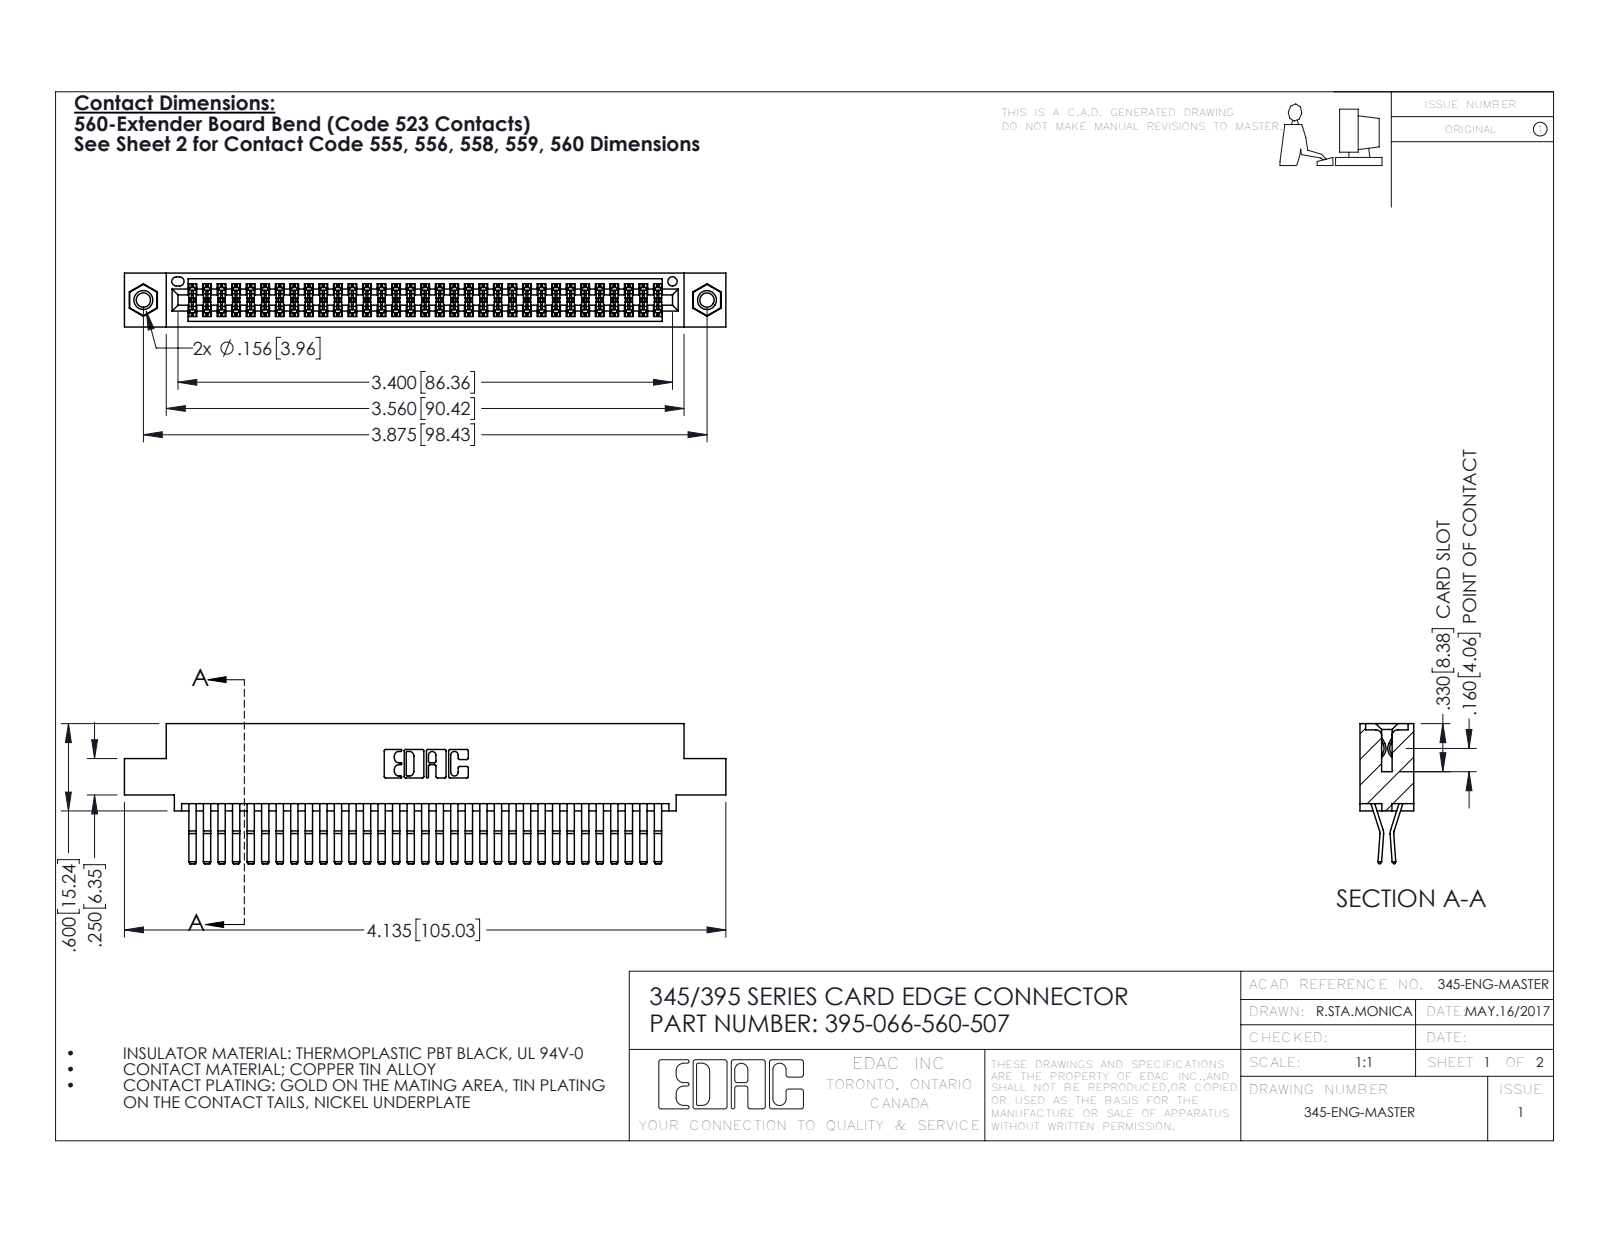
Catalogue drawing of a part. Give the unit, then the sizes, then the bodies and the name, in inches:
Units: inches
Overall size (bounding box): 4.135 × 0.962 × 0.37
Round holes (diameter × count): ⌀0.098 ×2, ⌀0.125 ×2, ⌀0.156 ×2, ⌀0.064 ×1
Round bosses / shafts (diameter × count): ⌀0.155 ×2
Partial cylindrical surfaces — rounded edges, fillets, slot ends (radius × count): R0.006 ×100, R0.01 ×22, R0.007 ×6, R0.031 ×6, R0.026 ×3, R0.01 ×2, R0.014 ×2, R0.019 ×2
Main face-to-face distances: 0.025, 0.072, 0.298, 0.2, 0.37, 0.098, 0.272, 0.225, 0.175, 0.149
Hole centre spacings: 0.27, 3.64, 3.875
Volume: 0.639 in³ · Surface area: 25.62 in²
Bodies: 69 solids, 3622 faces (2294 planar, 1312 cylindrical, 16 other)
Part name (STEP PRODUCT): 345-250-001_345-250-005-103; 345 Part_0.110 Offset - 0.156 Dia-TI; 395-066-560-507; 345-292-001_560 Tail
STEP written by: SolidWorks 2016 (CONFIG_CONTROL_DESIGN)
